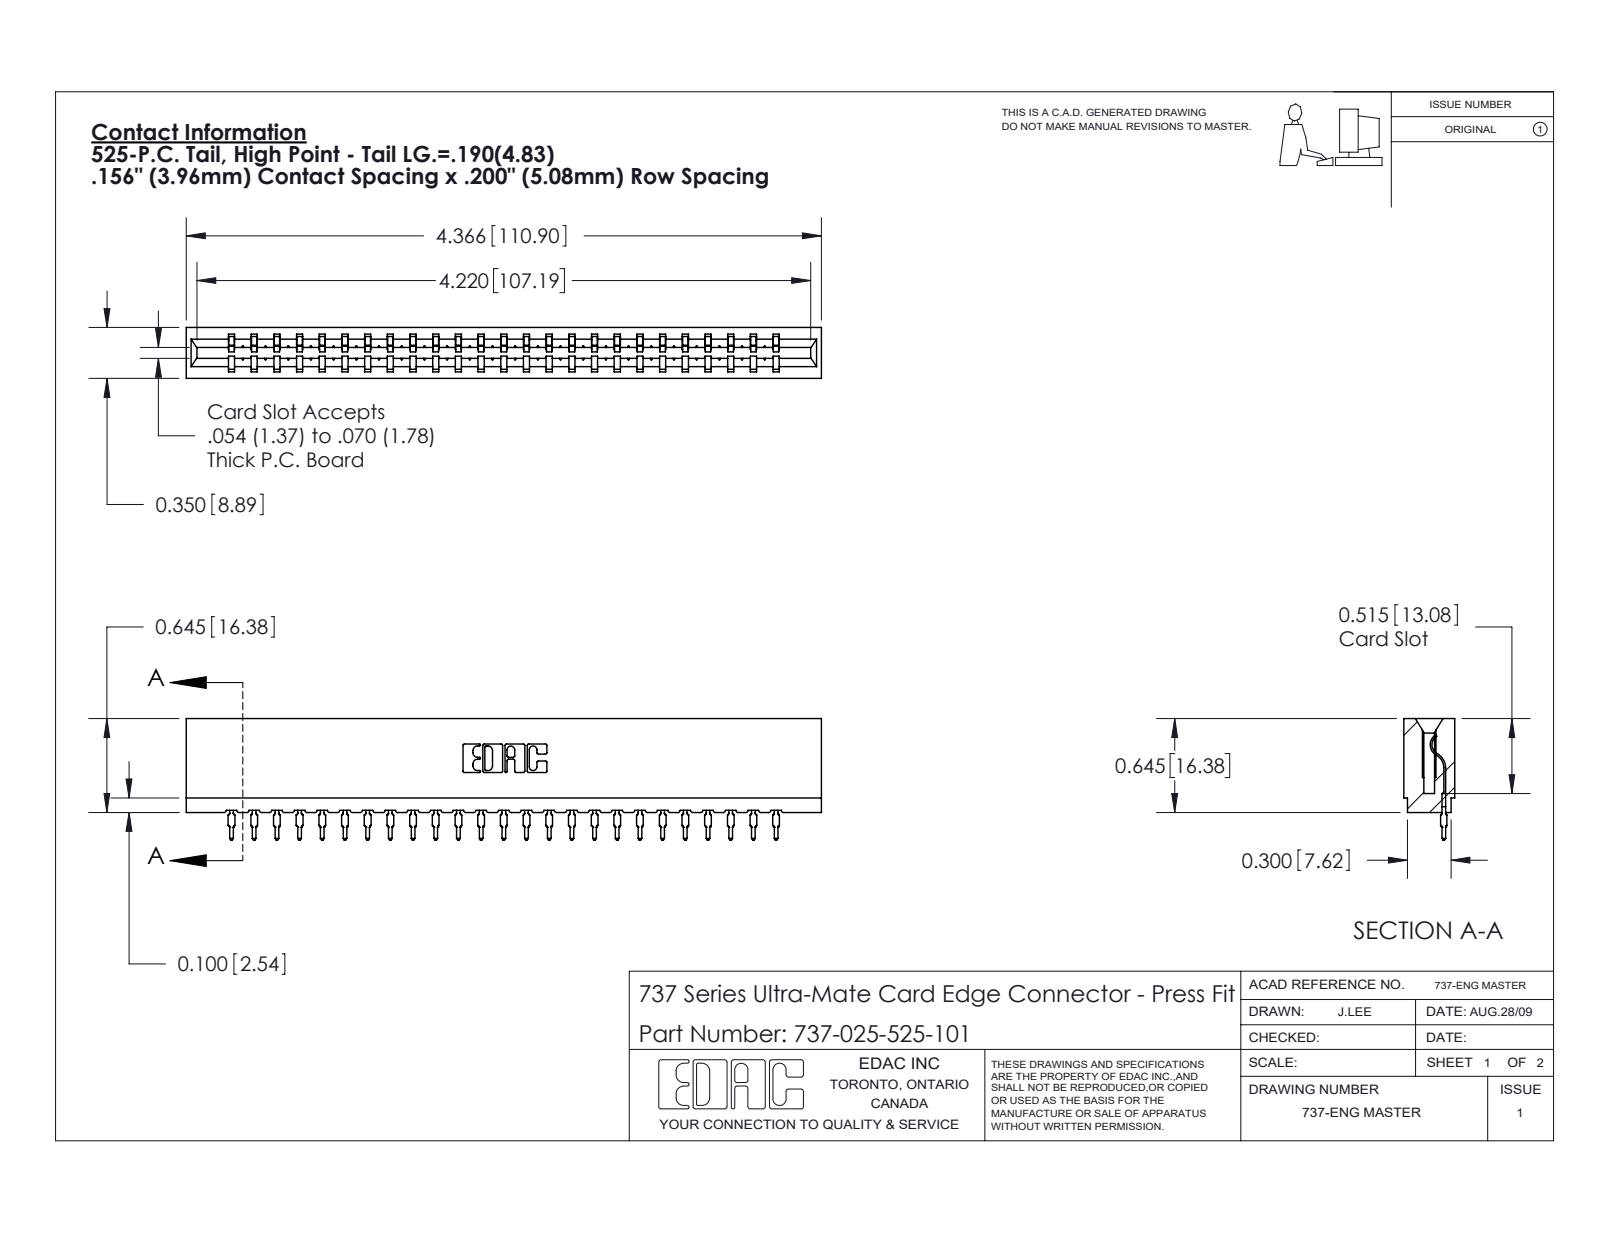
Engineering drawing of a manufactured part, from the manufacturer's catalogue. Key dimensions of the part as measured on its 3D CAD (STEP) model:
Part name (STEP PRODUCT): 745-292-001_525; 737 Part_Insulator Option - 01; 737-025-525-101
STEP written by: SolidWorks 2020 (CONFIG_CONTROL_DESIGN)
Units: inches
Bodies: 26 solids, 2919 faces (1754 planar, 515 cylindrical, 650 other)
Overall size (bounding box): 4.366 × 0.836 × 0.35
Volume: 0.66 in³ · Surface area: 21.94 in²
Partial cylindrical surfaces — rounded edges, fillets, slot ends (radius × count): R0.015 ×50, R0.021 ×50, R0.01 ×22, R0.007 ×6, R0.031 ×6, R0.005 ×4, R0.011 ×4, R0.026 ×3
Main face-to-face distances: 0.138, 0.212, 0.35, 0.156, 0.624, 0.074, 0.468, 0.78, 0.045, 0.305
